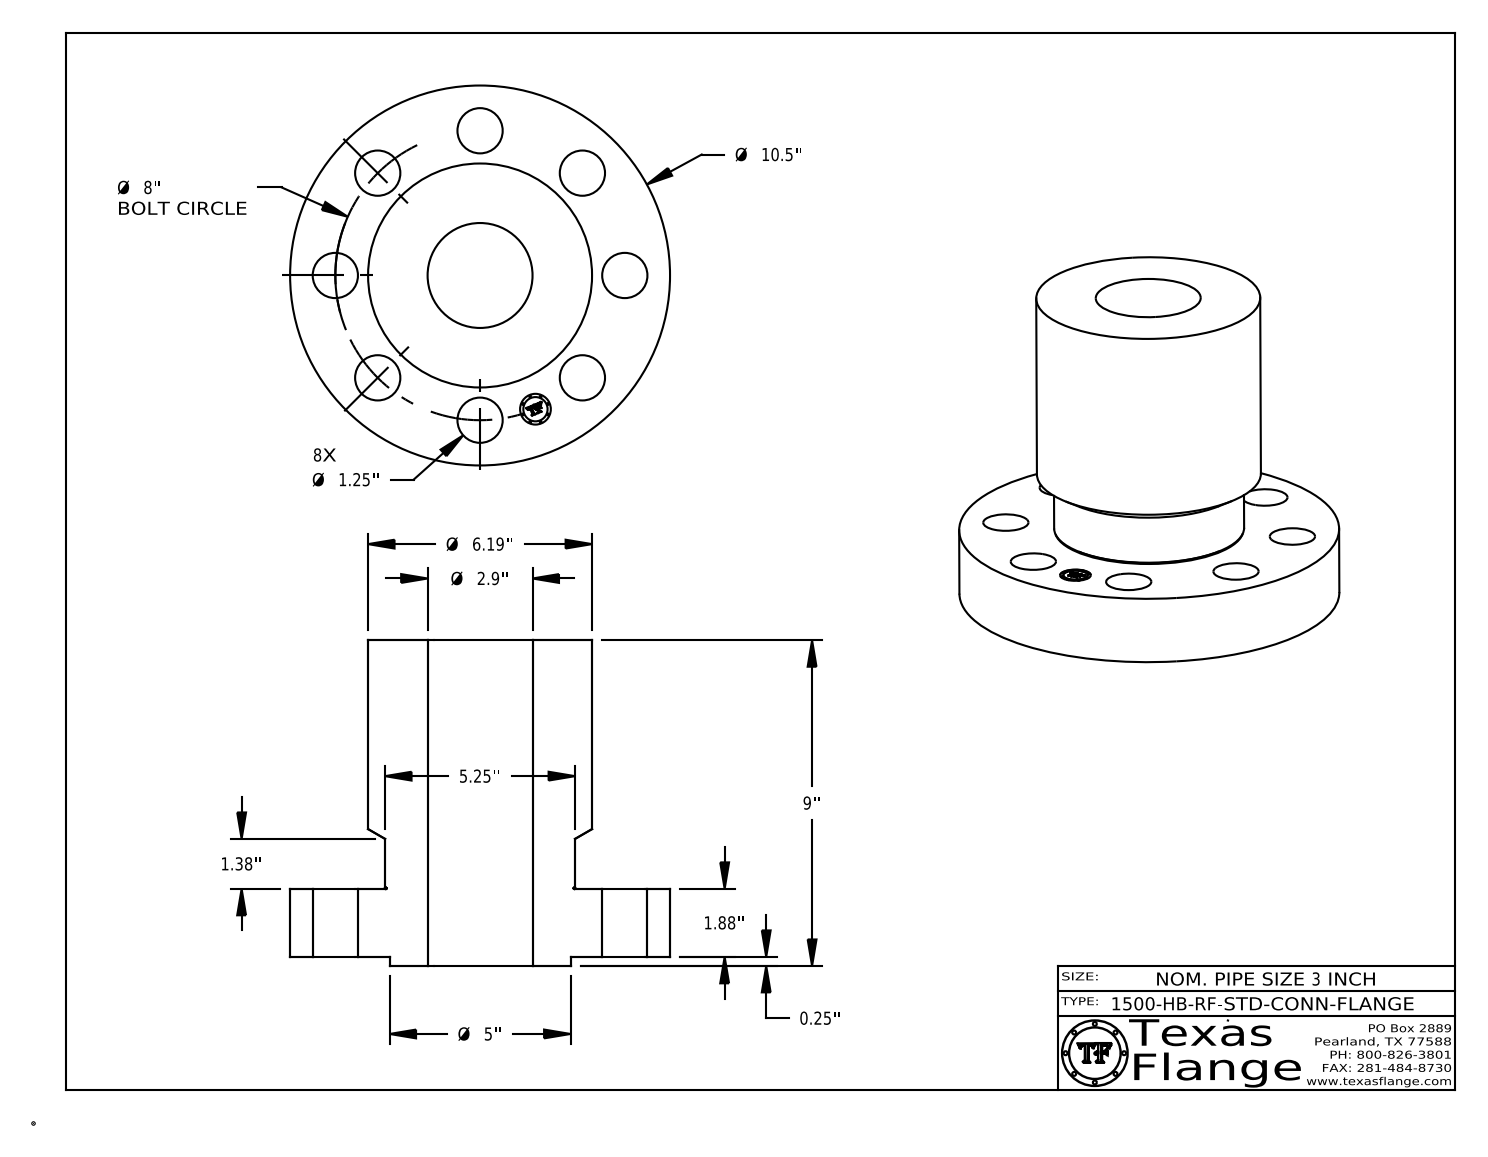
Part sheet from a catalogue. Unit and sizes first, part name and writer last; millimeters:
Units: millimetres
Overall size (bounding box): 266.7 × 266.7 × 228.6
Round holes (diameter × count): ⌀31.8 ×8, ⌀21.6 ×1, ⌀73.7 ×1
Round bosses / shafts (diameter × count): ⌀1.3 ×8, ⌀266.7 ×1, ⌀157.2 ×1, ⌀133.4 ×1, ⌀127 ×1, ⌀17 ×1
Main face-to-face distances: 47.8, 222.3, 174.5, 6.4, 54.1, 228.6, 54, 47.6, 174.6, 6.5
Hole centre spacings: 101.6, 77.7, 143.7, 187.7, 39.6, 169, 199.3, 203.2
Volume: 4 649 000 mm³ · Surface area: 316 500 mm²
Bodies: 1 solid, 421 faces (369 planar, 46 cylindrical, 6 other)
Part name (STEP PRODUCT): 3-1500-HB-RF-STD-CONN-FLANGE
STEP written by: CATIA V5 STEP AP214 (AUTOMOTIVE_DESIGN)
